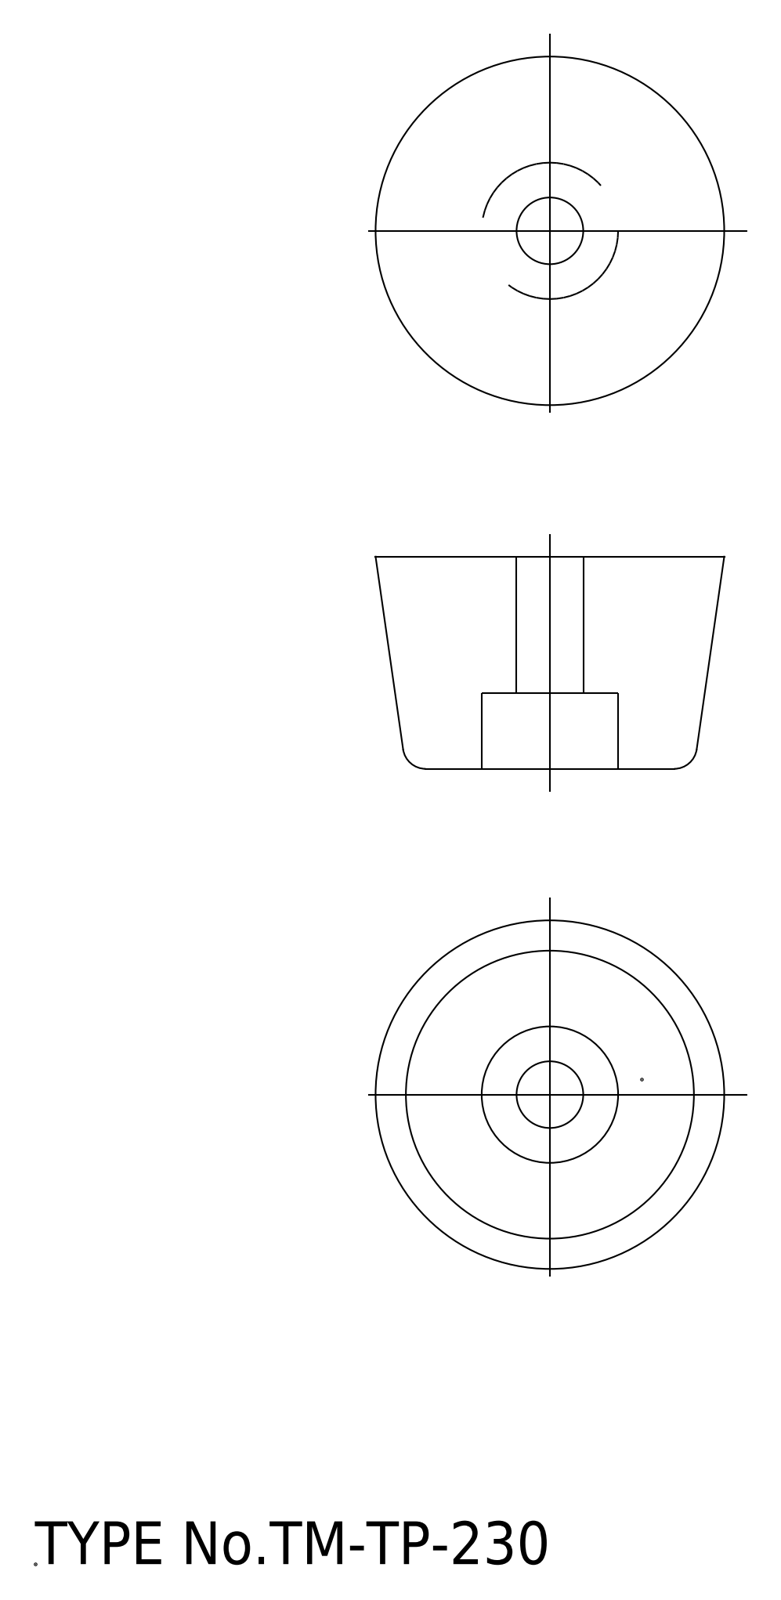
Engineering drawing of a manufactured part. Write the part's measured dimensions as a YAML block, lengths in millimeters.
step_written_by: "spGate 19.8.4 (****-****-****-****) (AUTOMOTIVE_DESIGN)"
units: millimeters
bodies: {solids: 1, faces: 11, planar: 3, cylindrical: 4, other: 4}
overall_size: [23, 23, 14]
volume: 4398
surface_area: 1841
round_holes:
  - {diameter: 4.4, count: 1}
  - {diameter: 9, count: 1}
face_to_face_distances: [14, 5, 9]
